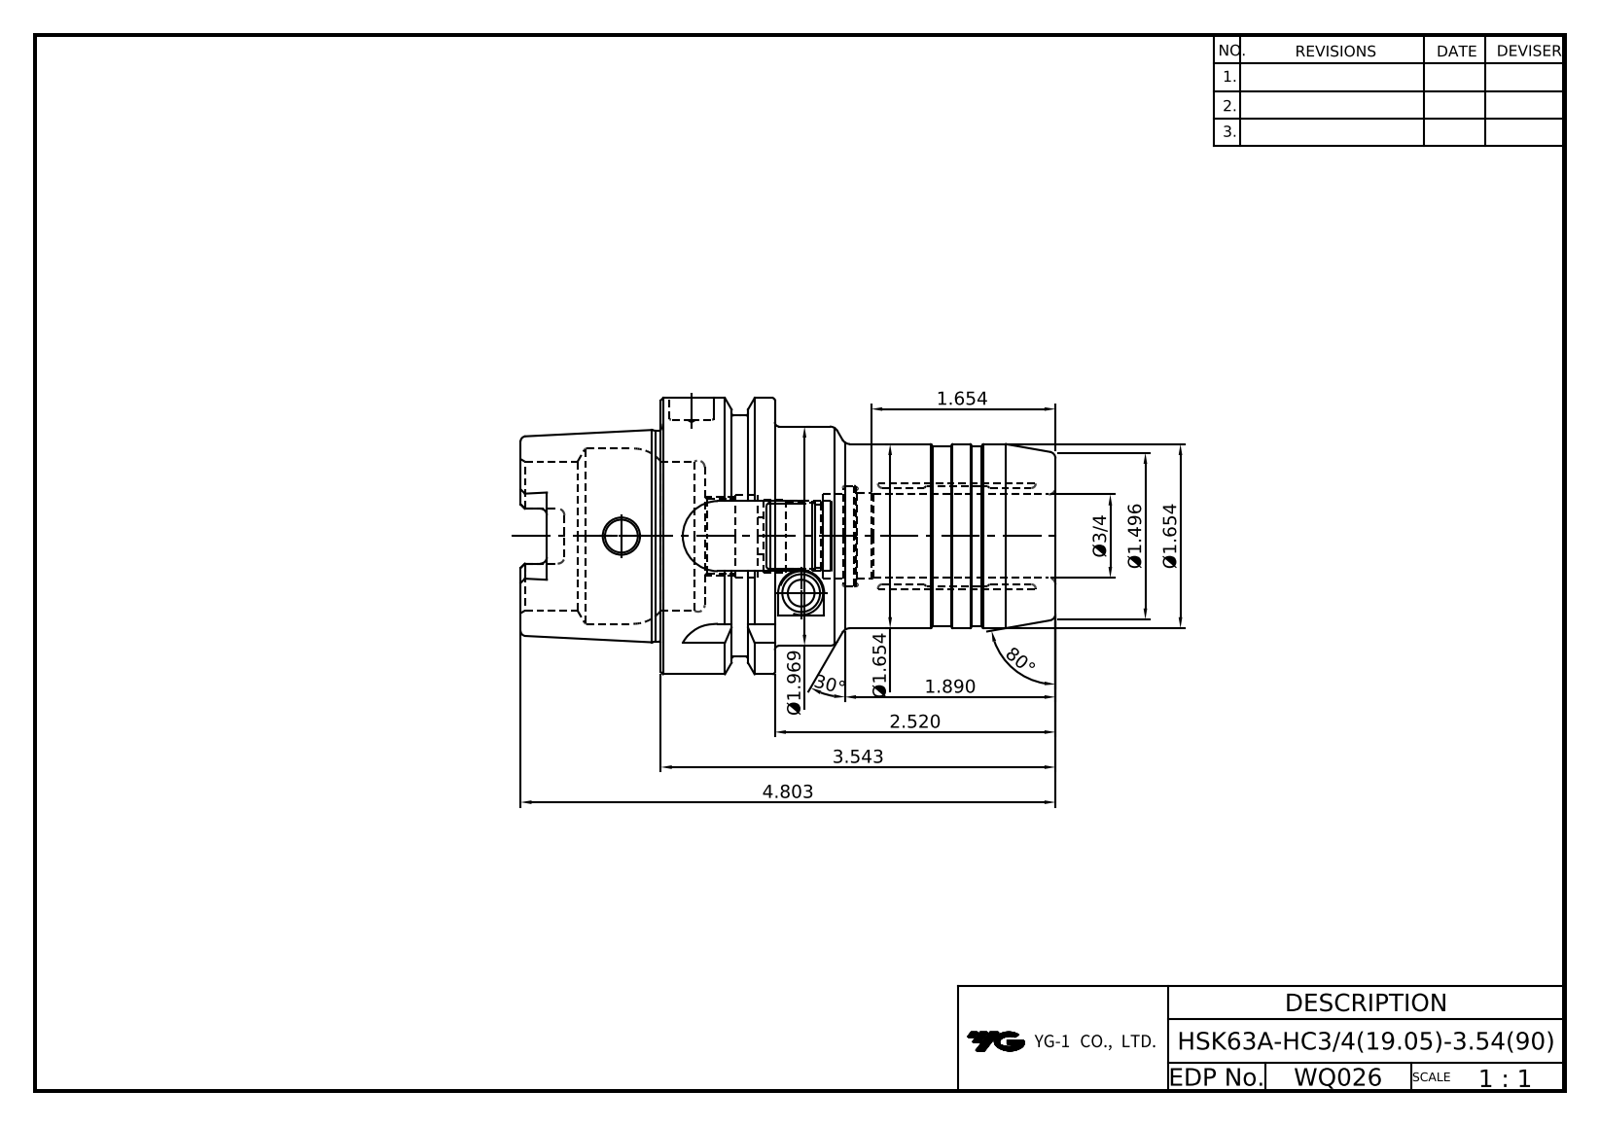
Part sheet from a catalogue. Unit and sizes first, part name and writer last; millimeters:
Units: millimetres
Overall size (bounding box): 122 × 63 × 63
Round holes (diameter × count): ⌀10 ×2, ⌀7.5 ×1, ⌀8.4 ×1, ⌀15 ×1, ⌀16 ×1, ⌀16.6 ×1, ⌀17 ×1, ⌀18 ×1, ⌀19 ×1, ⌀19.05 ×1, ⌀19.4 ×1, ⌀19.5 ×1
Round bosses / shafts (diameter × count): ⌀63 ×1, ⌀55 ×1, ⌀50 ×1, ⌀48.04 ×1, ⌀42 ×1, ⌀41 ×1
Partial cylindrical surfaces — rounded edges, fillets, slot ends (radius × count): R1.5 ×6, R2.88 ×4, R8 ×4, R5.25 ×1
Main face-to-face distances: 26, 90, 64, 10, 16, 80, 32, 53, 6.12, 9.88
Hole centre spacings: 43.01
Volume: 158 155 mm³ · Surface area: 35 497 mm²
Bodies: 1 solid, 232 faces (70 planar, 70 cylindrical, 92 other)
Part name (STEP PRODUCT): WQ026-HSK63A-HC0_75-3_54
STEP written by: CREO PARAMETRIC BY PTC INC, 2018100 (CONFIG_CONTROL_DESIGN)
